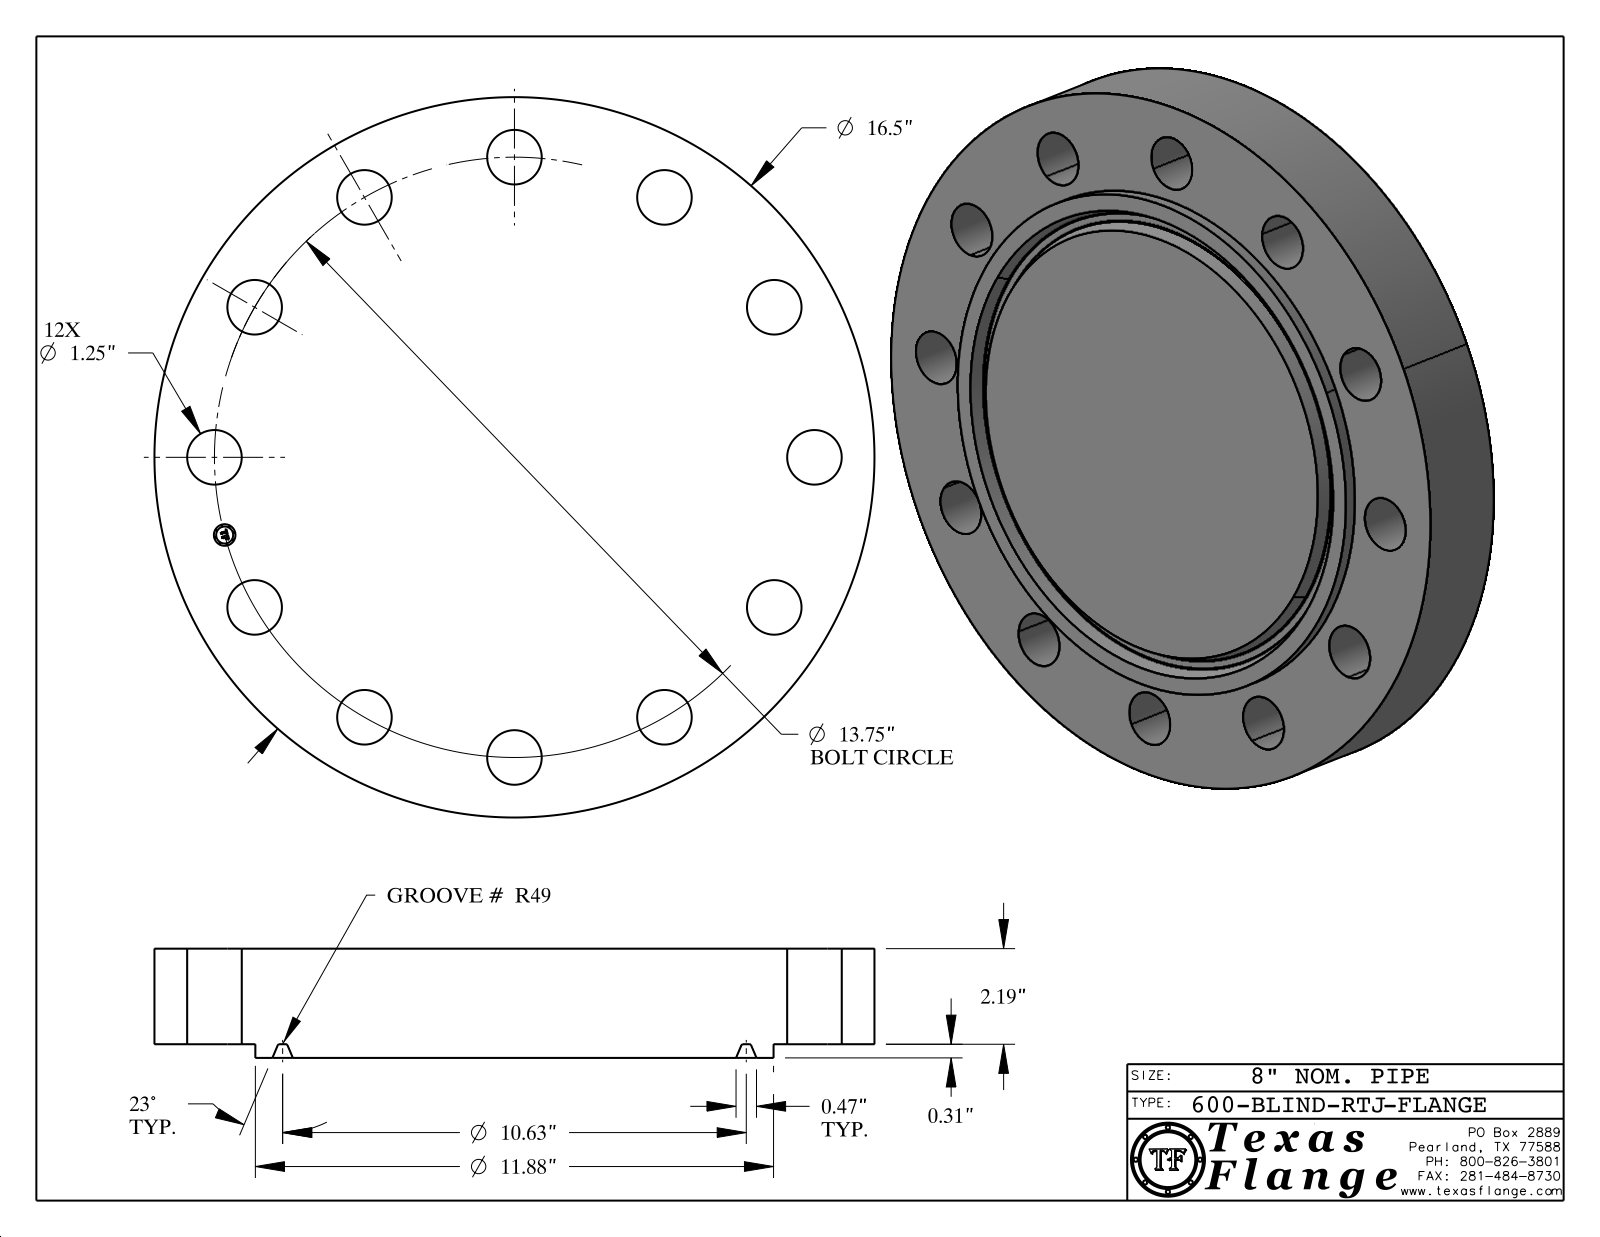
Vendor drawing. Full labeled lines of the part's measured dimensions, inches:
Part name (STEP PRODUCT): 600-BLIND-RTJ
STEP written by: CATIA V5 STEP AP214 (AUTOMOTIVE_DESIGN)
Units: inches
Bodies: 1 solid, 426 faces (370 planar, 48 cylindrical, 8 other)
Overall size (bounding box): 16.5 × 16.5 × 2.503
Volume: 467.1 in³ · Surface area: 640.2 in²
Round holes (diameter × count): ⌀1.25 ×12, ⌀0.495 ×1
Round bosses / shafts (diameter × count): ⌀0.03 ×8, ⌀16.5 ×1, ⌀11.875 ×1, ⌀0.39 ×1
Main face-to-face distances: 2.503, 0.313, 2.19, 2.488, 2.175, 0.015, 0.148, 0.145, 0.027, 0.096
Hole centre spacings: 9.723, 11.908, 13.281, 3.559, 6.875, 3.559, 6.875, 13.75
